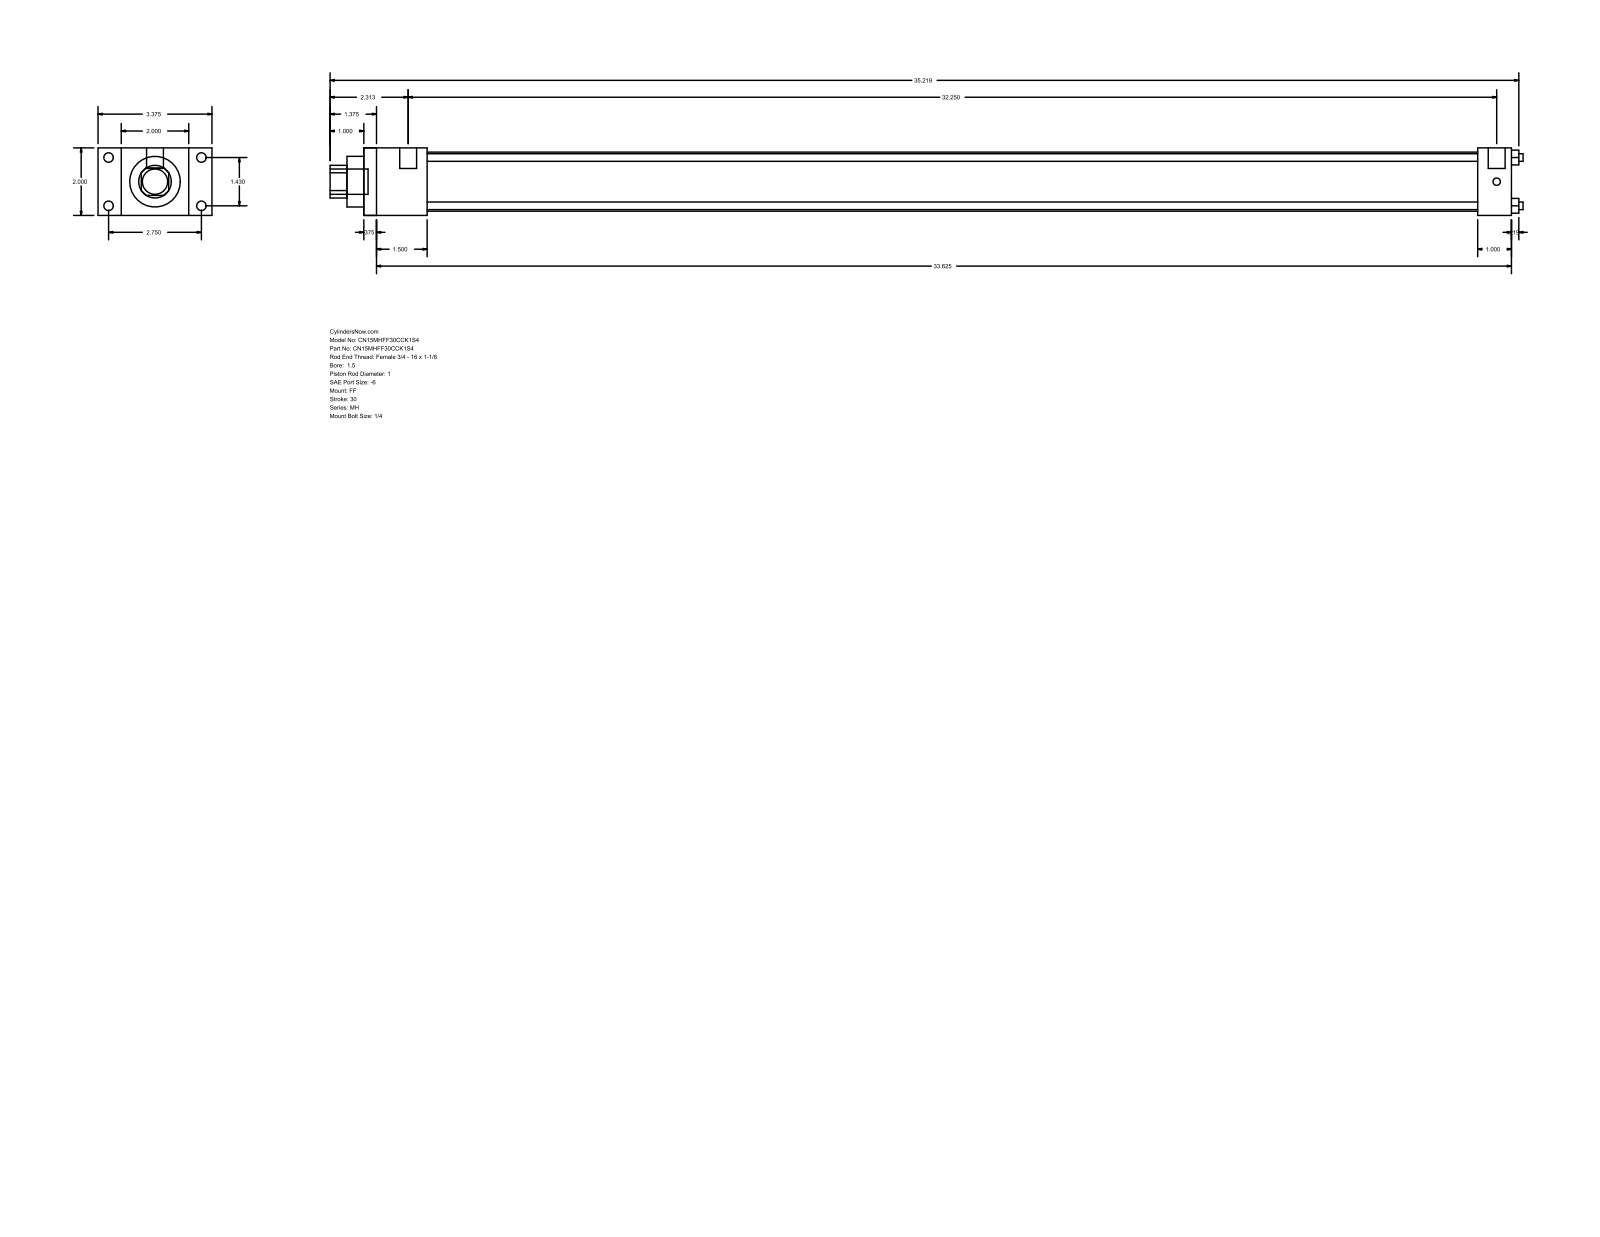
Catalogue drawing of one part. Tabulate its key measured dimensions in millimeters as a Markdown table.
| quantity | value |
| --- | --- |
| part name | MH_FF__0150_1 |
| STEP written by | GSSL Pune (CONFIG_CONTROL_DESIGN) |
| units | millimeters |
| bodies | 0 solids, 92 faces (64 planar, 28 cylindrical, 0 other) |
| overall size | 897.73 × 85.72 × 50.8 |
| round holes (diameter × count) | 5.71 × 4, 25.4 × 1, 38.1 × 1, 44.45 × 1 |
| round bosses / shafts (diameter × count) | 7.14 × 4, 5.56 × 4, 12.7 × 2, 19.05 × 1 |
| partial cylindrical surfaces (radius × count) | 12.29 × 1 |
| main face-to-face distances | 50.8, 863.6, 9.52, 854.08, 25.4, 17.46, 68.26, 47.63, 38.11, 815.97 |
| hole center spacings | 25.68, 36.32, 51.36 |
